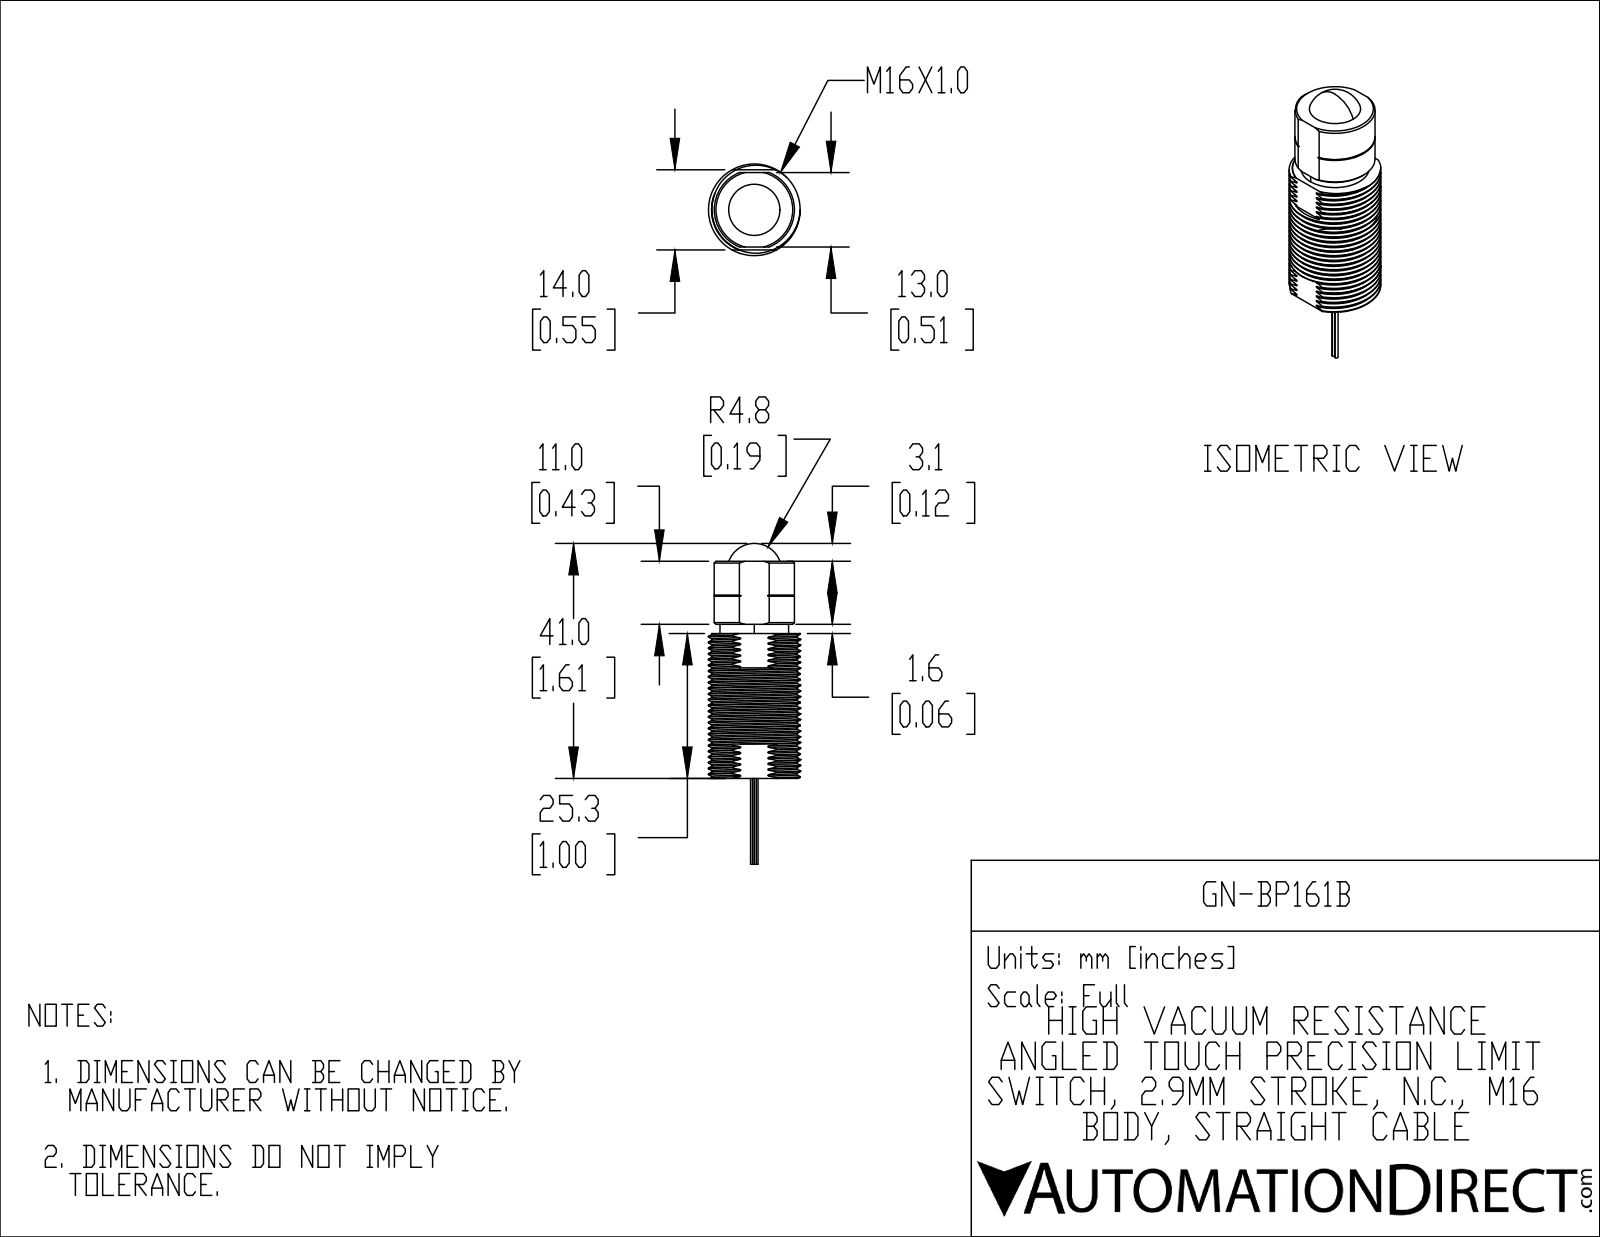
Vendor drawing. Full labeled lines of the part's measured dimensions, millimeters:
Part name (STEP PRODUCT): GN-BP161B
STEP written by: SolidWorks 2020 (CONFIG_CONTROL_DESIGN)
Units: millimetres
Bodies: 1 solid, 163 faces (16 planar, 62 cylindrical, 85 other)
Overall size (bounding box): 56.01 × 16 × 16
Volume: 6 577 mm³ · Surface area: 3 002 mm²
Round bosses / shafts (diameter × count): ⌀0.6 ×2, ⌀16 ×1, ⌀12 ×1
Partial cylindrical surfaces — rounded edges, fillets, slot ends (radius × count): R7 ×1
Main face-to-face distances: 0.5, 13.5, 37.9, 14, 12.6, 25.3, 13, 11, 1.6, 26.9
